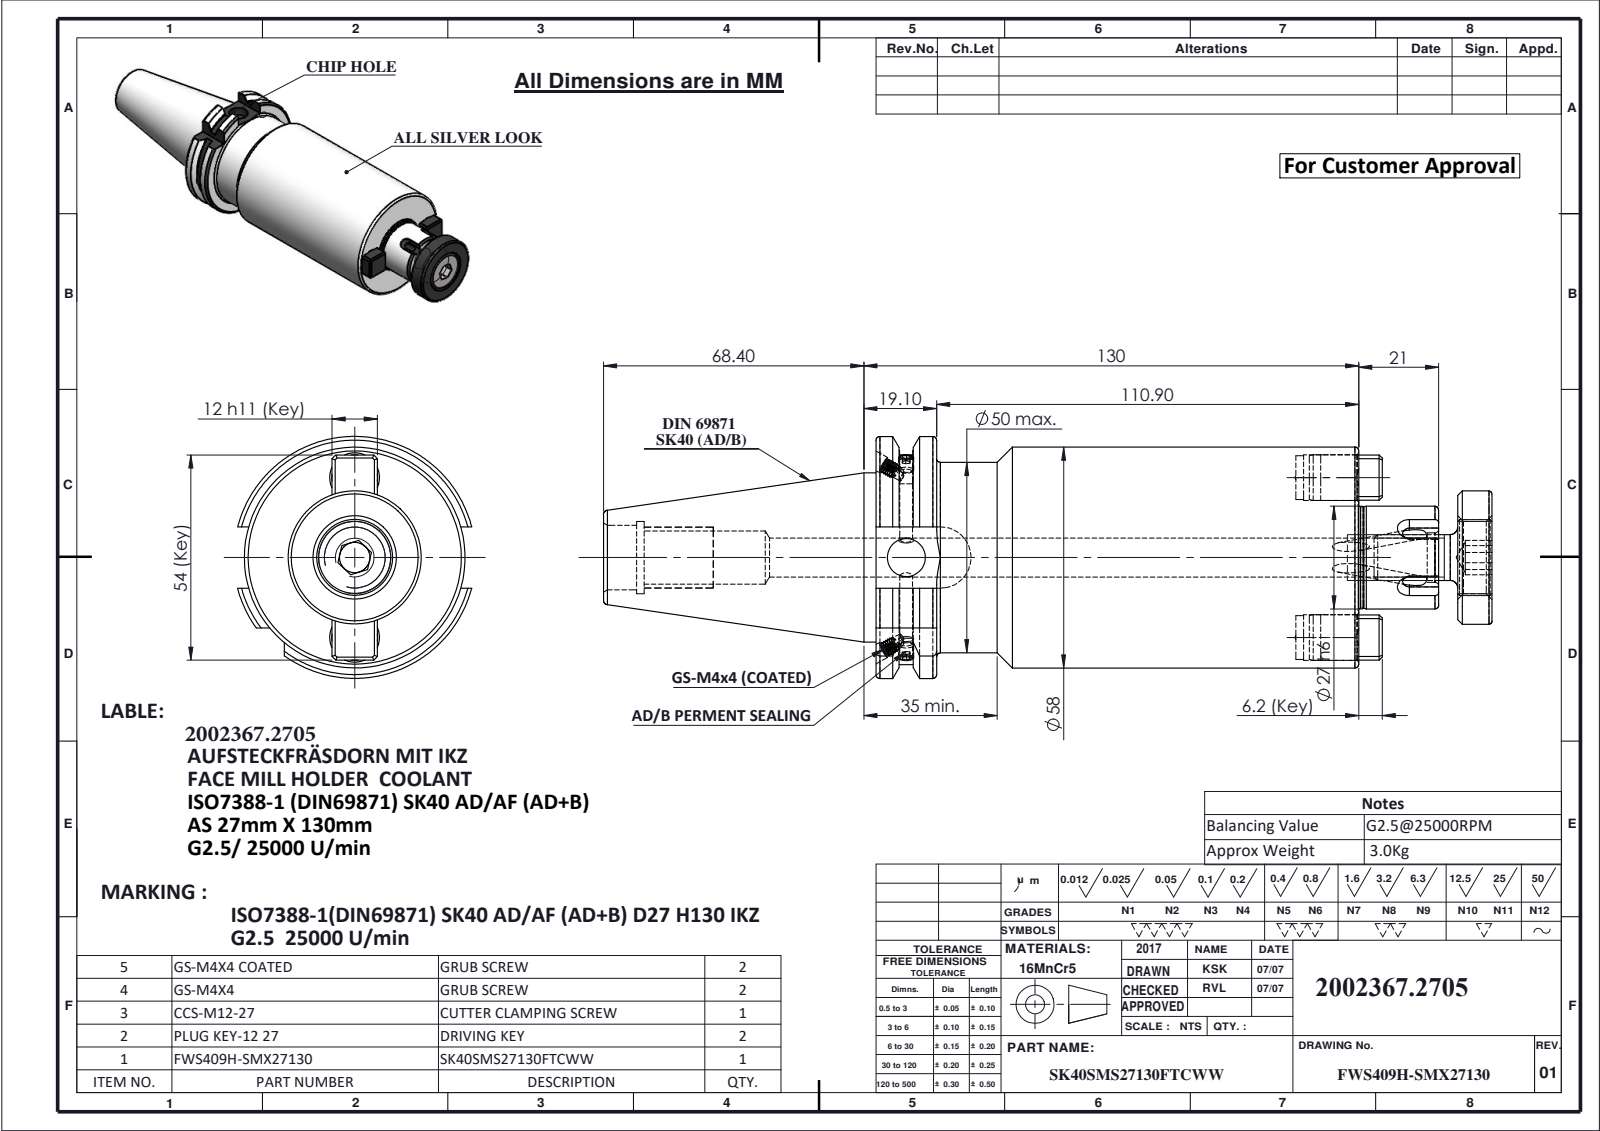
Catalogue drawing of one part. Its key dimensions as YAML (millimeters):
part_name: "CCS-M12-27-1; CCS-M12-27; GS-M4X4-COATING_DIN 913 - M4 x 4-N; SK40SMS27130FWW (+4 more)"
step_written_by: "SolidWorks 2024 (CONFIG_CONTROL_DESIGN)"
units: millimeters
bodies: {solids: 9, faces: 421, planar: 132, cylindrical: 120, other: 169}
overall_size: [233.4, 63.55, 61.48]
volume: 393950
surface_area: 56526
round_holes:
  - {diameter: 3, count: 4}
  - {diameter: 3.3, count: 3}
  - {diameter: 4.5, count: 2}
  - {diameter: 11.5, count: 2}
  - {diameter: 12, count: 2}
  - {diameter: 10, count: 1}
  - {diameter: 10.2, count: 1}
  - {diameter: 13, count: 1}
  - {diameter: 14, count: 1}
  - {diameter: 17, count: 1}
  - {diameter: 19, count: 1}
round_bosses_or_shafts:
  - {diameter: 4, count: 4}
  - {diameter: 12.02, count: 2}
  - {diameter: 12.02, count: 2}
  - {diameter: 58, count: 1}
  - {diameter: 50, count: 1}
  - {diameter: 44.45, count: 1}
  - {diameter: 35, count: 1}
  - {diameter: 27, count: 1}
partial_cylinders:
  - {radius: 2, count: 4}
  - {radius: 7.75, count: 2}
  - {radius: 8.05, count: 1}
  - {radius: 28.12, count: 1}
  - {radius: 31.77, count: 1}
face_to_face_distances: [126.8, 35, 161.8, 15.9, 110.9, 145.9, 152.8, 136.9, 26, 9]
hole_center_spacings: [21, 42]
